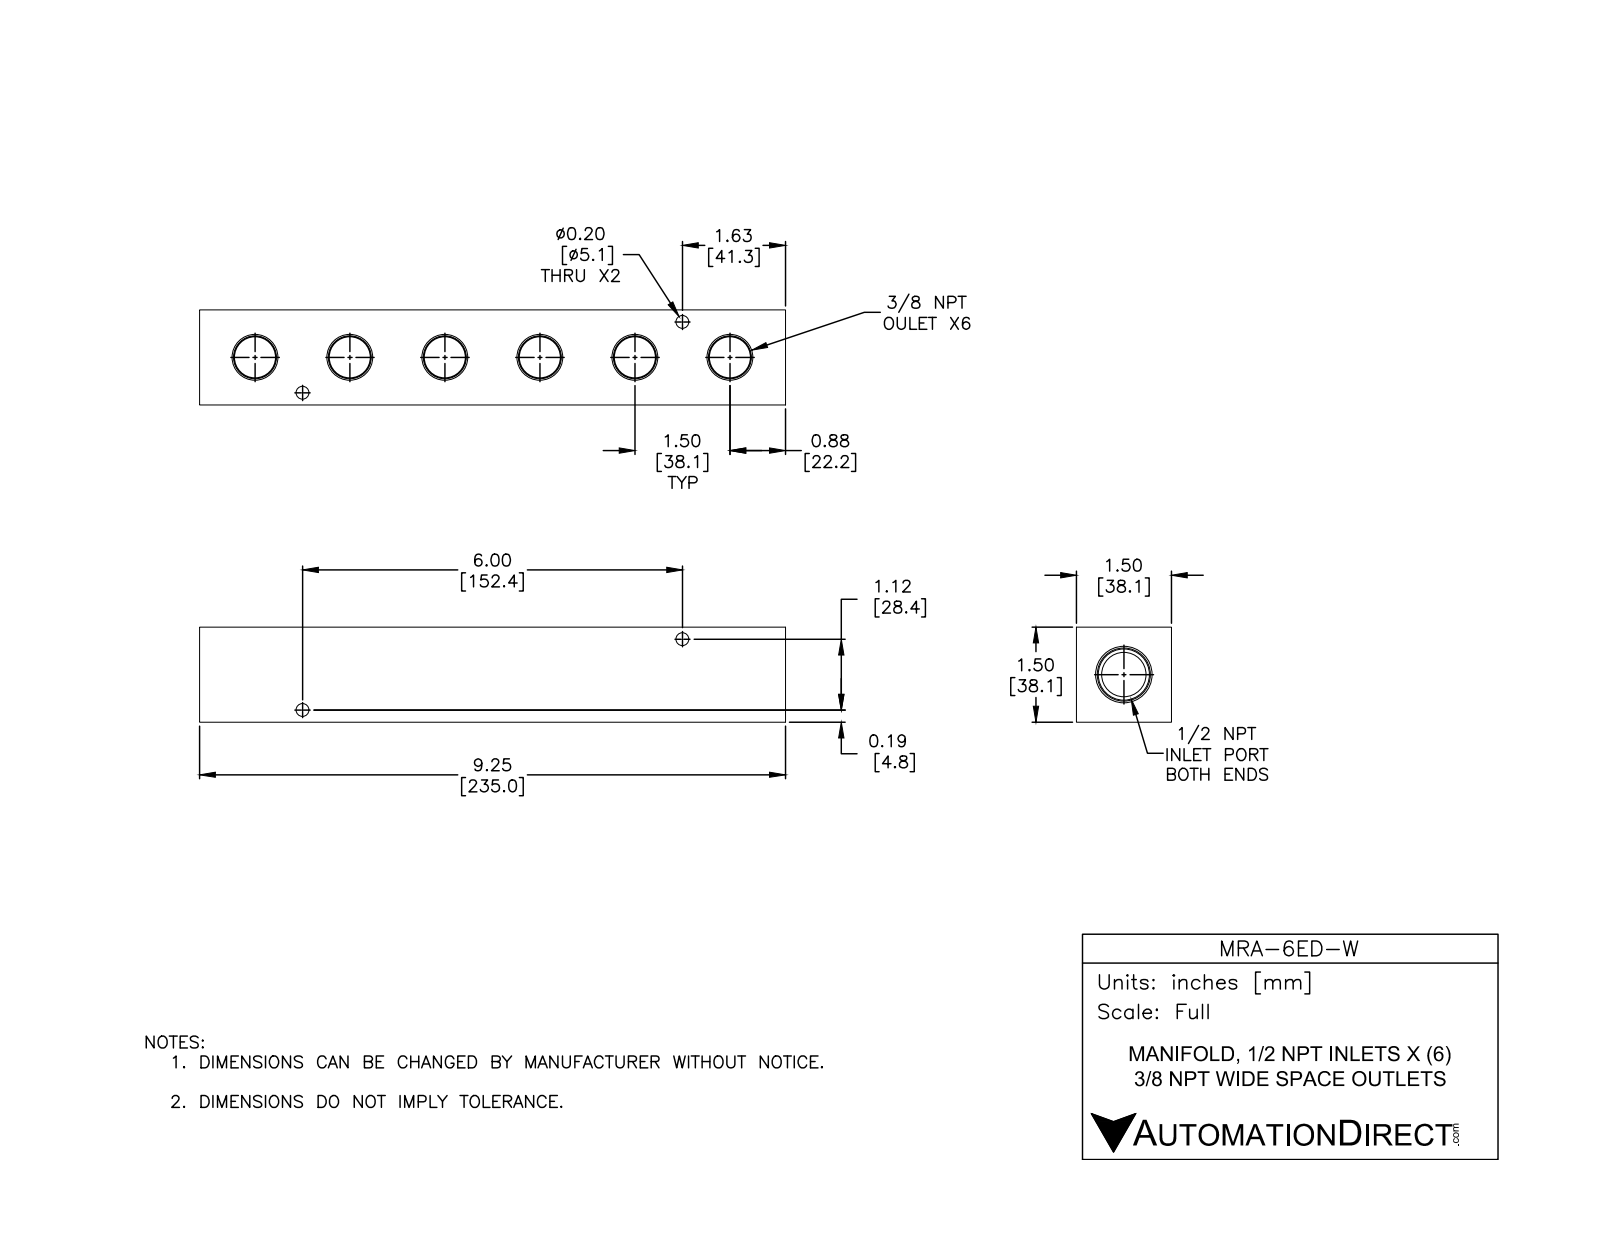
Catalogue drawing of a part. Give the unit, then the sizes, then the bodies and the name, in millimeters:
Units: millimetres
Overall size (bounding box): 235 × 38.1 × 38.1
Round holes (diameter × count): ⌀14.3 ×6, ⌀5.1 ×4, ⌀17.9 ×1
Main face-to-face distances: 38.1, 235, 27.7, 10.4, 13.5, 221.5, 208
Hole centre spacings: 38.1, 76.2, 114.3, 23.7, 23.9, 152.4, 155, 58.8
Volume: 262 200 mm³ · Surface area: 54 940 mm²
Bodies: 1 solid, 82 faces (20 planar, 30 cylindrical, 32 other)
Part name (STEP PRODUCT): MRA-6ED-W
STEP written by: SolidWorks 2015 (CONFIG_CONTROL_DESIGN)
